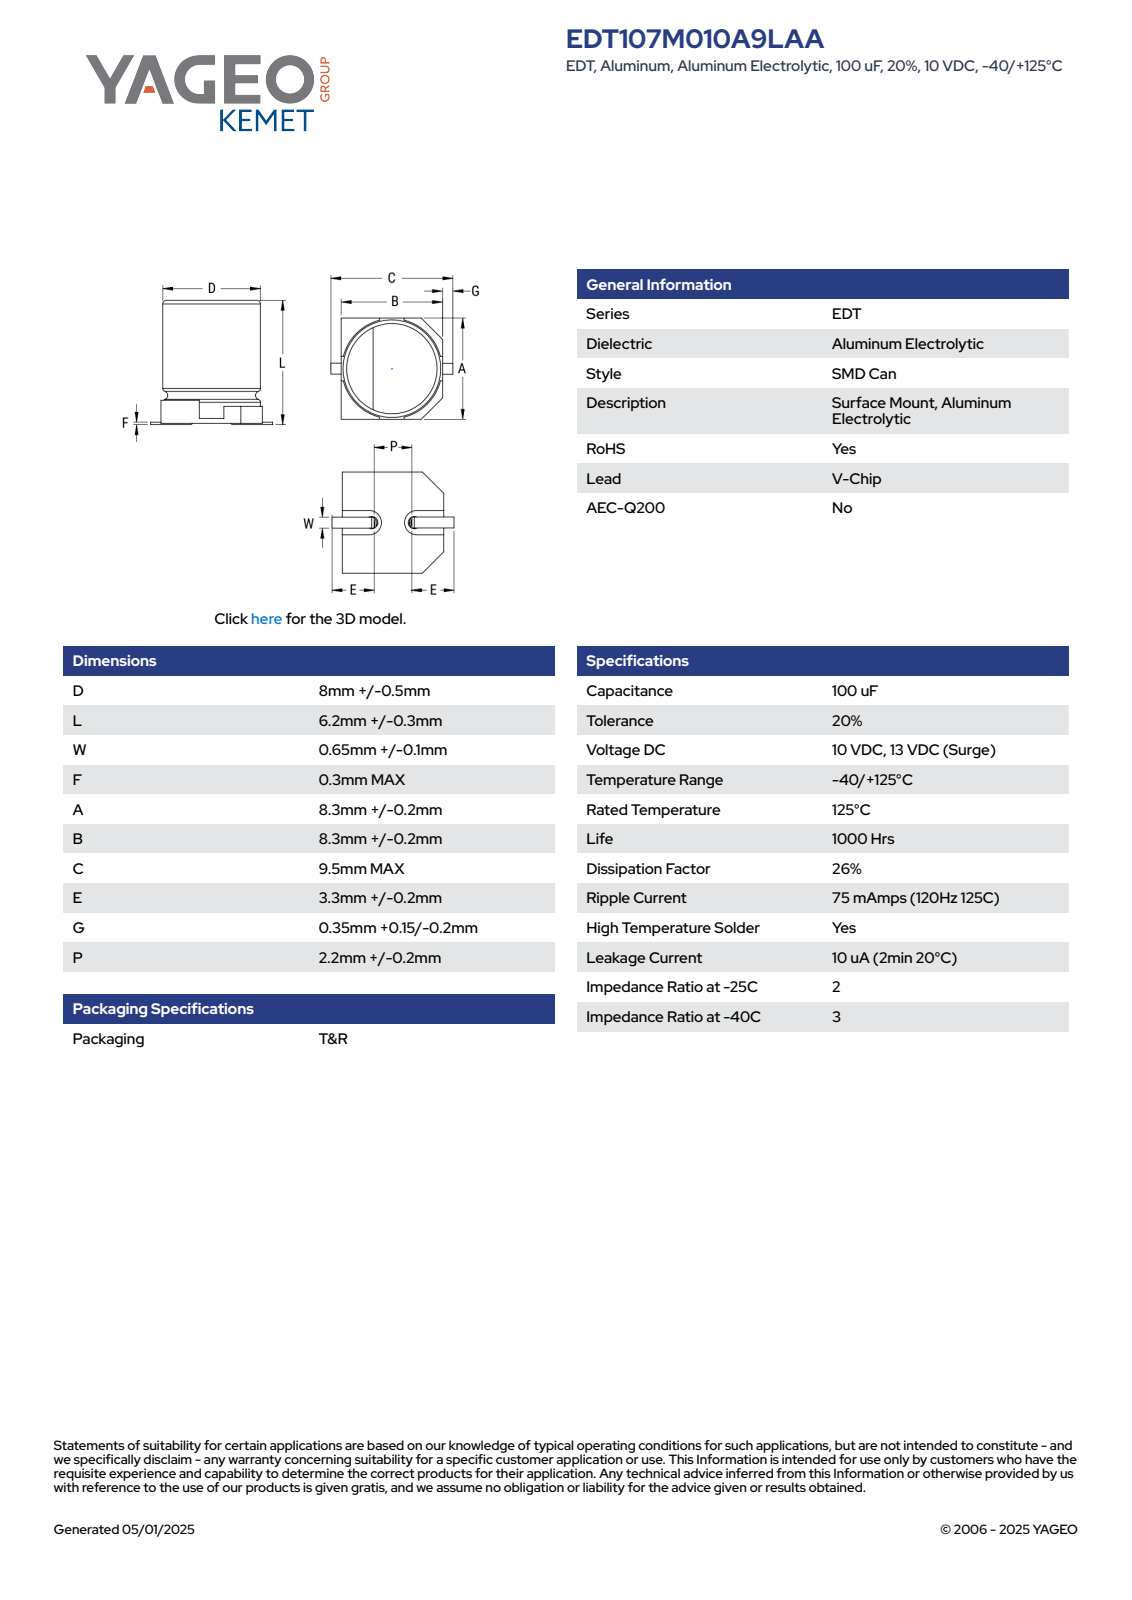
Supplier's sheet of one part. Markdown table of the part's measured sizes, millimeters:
| quantity | value |
| --- | --- |
| part name | CAC_S_8X6.2_D8.5L6.5W0.75F0.3A8.5B8.5C9.5E3.6P2.4 |
| STEP written by | SolidWorks 2014 (AUTOMOTIVE_DESIGN) |
| units | millimeters |
| bodies | 5 solids, 78 faces (61 planar, 11 cylindrical, 6 other) |
| overall size | 9.6 × 8.5 × 6.5 |
| volume | 337 mm³ |
| surface area | 453 mm² |
| round bosses / shafts (diameter × count) | 8.13 × 1 |
| partial cylindrical surfaces (radius × count) | 0.2 × 2, 3.38 × 1, 4.25 × 1 |
| main face-to-face distances | 0.33, 6.2, 5.87, 8.5, 1.62, 1.29, 4.58, 0.75, 0.63, 1.92 |
